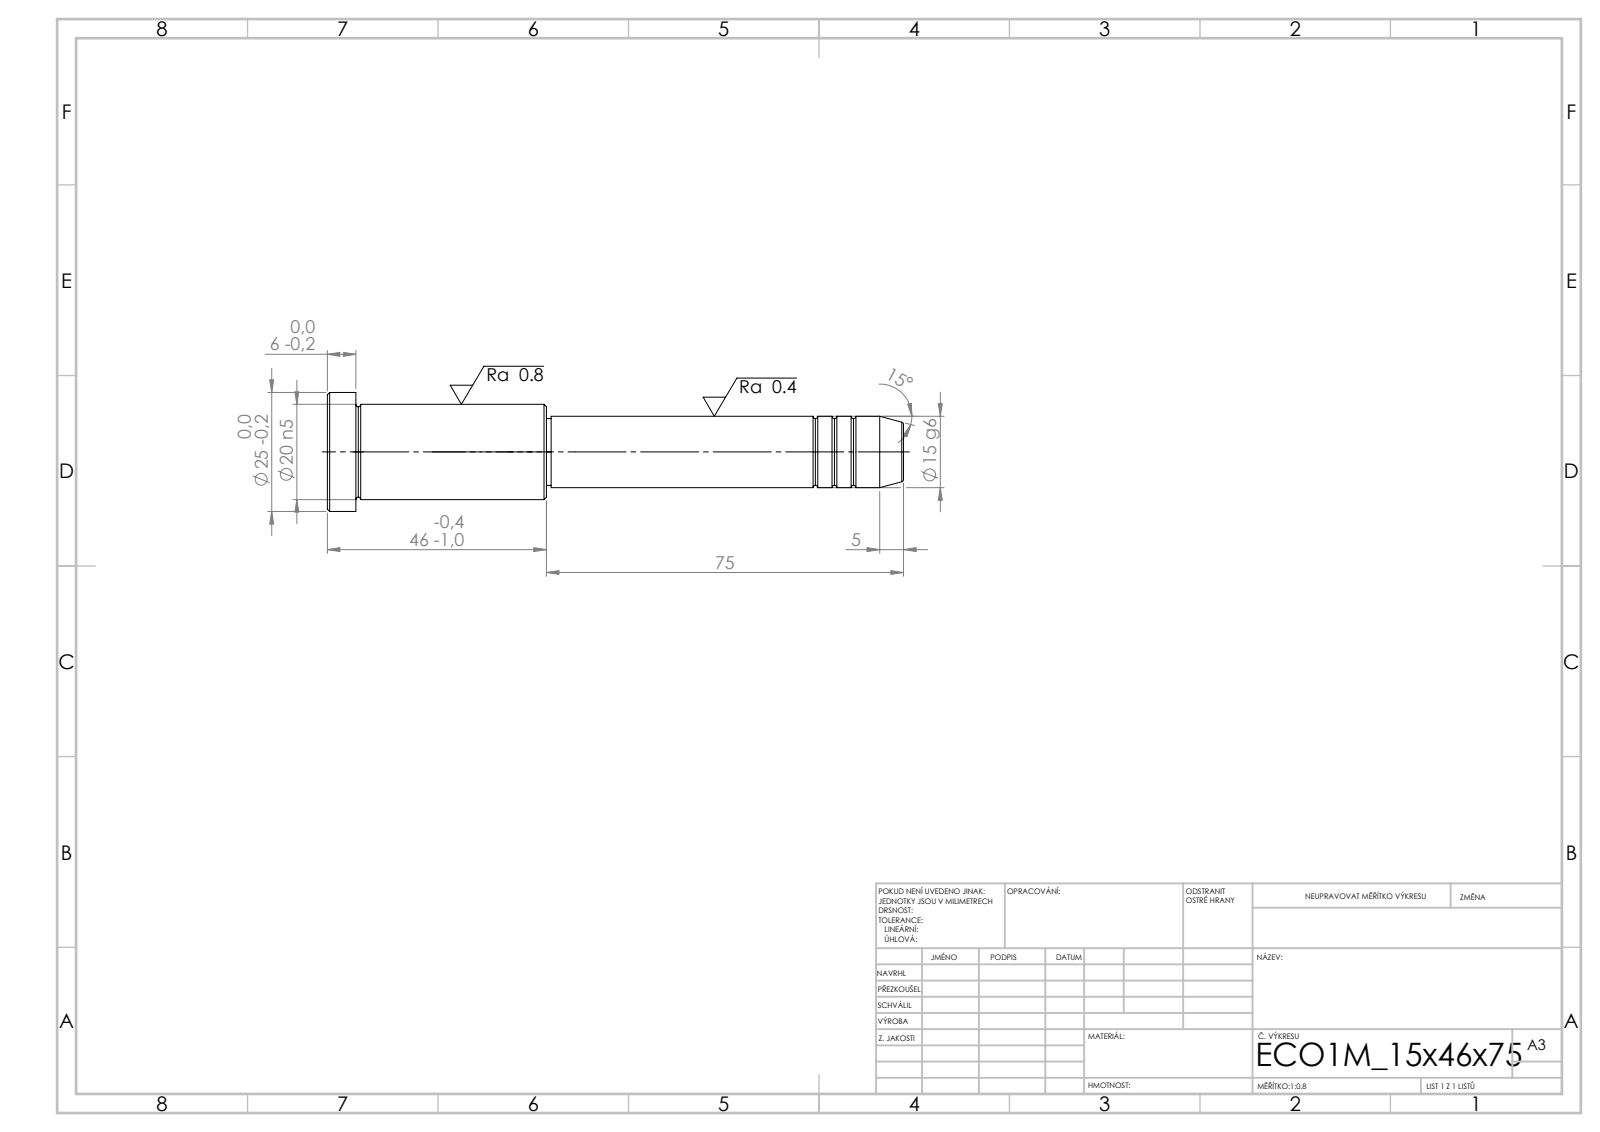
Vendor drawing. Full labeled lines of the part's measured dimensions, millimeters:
STEP written by: SolidWorks 2019 (CONFIG_CONTROL_DESIGN)
Units: millimetres
Bodies: 1 solid, 43 faces (5 planar, 14 cylindrical, 24 other)
Overall size (bounding box): 121 × 25 × 25
Volume: 28 497 mm³ · Surface area: 7 529 mm²
Round bosses / shafts (diameter × count): ⌀25 ×1, ⌀20 ×1, ⌀15 ×1, ⌀14 ×1
Main face-to-face distances: 6, 40, 46, 75, 115, 121, 74, 1, 41, 47
